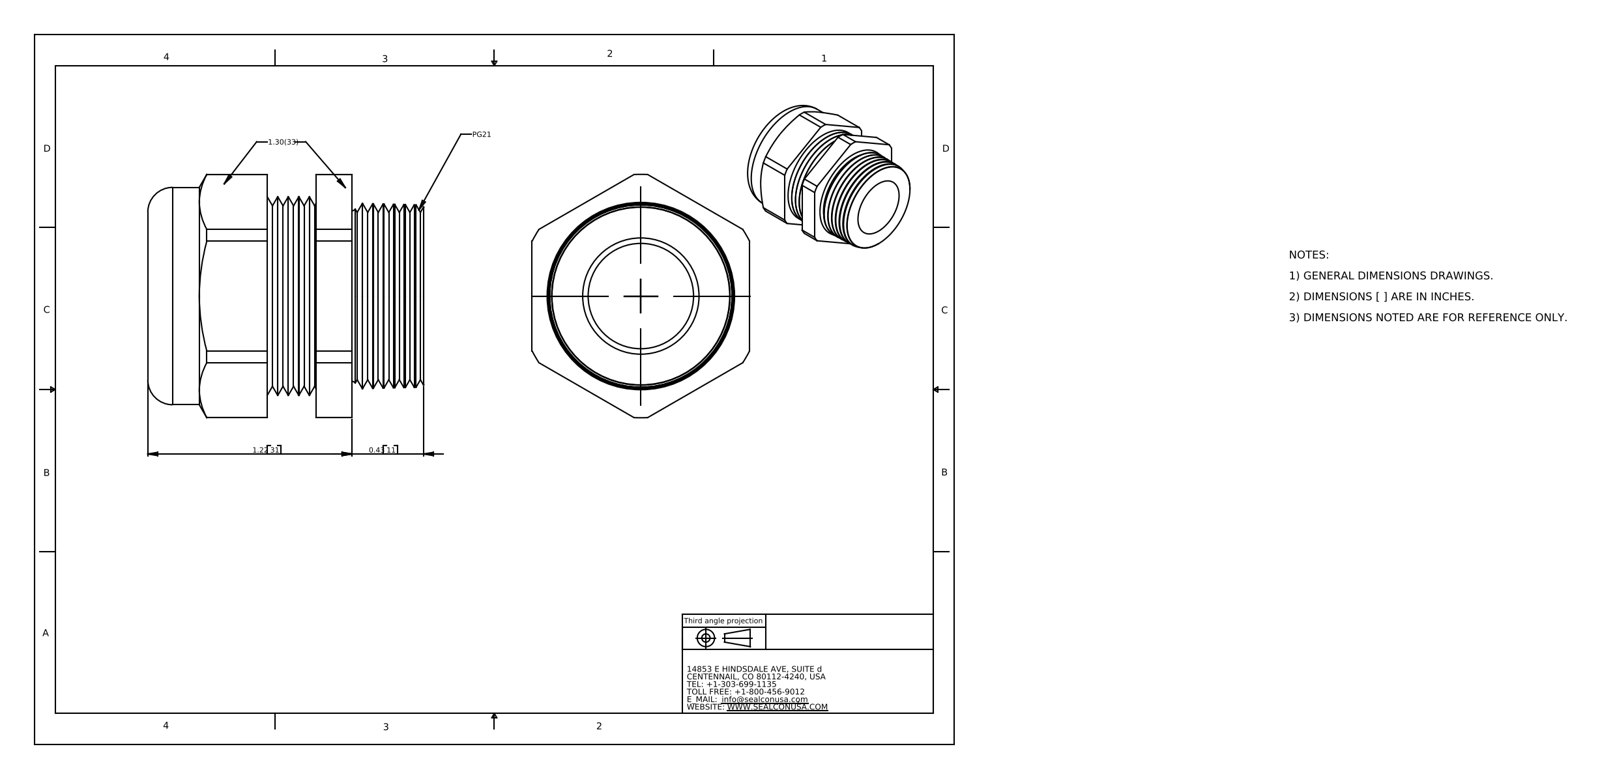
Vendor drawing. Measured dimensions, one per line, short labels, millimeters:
name: CD21AR-GY
written by: SolidWorks 2007 (CONFIG_CONTROL_DESIGN)
unit: mm
bodies: 2 solids, 130 faces (20 planar, 32 cylindrical, 78 other)
size: 41.9 × 37 × 33
volume: 22 990 mm³; area: 11 330 mm²
holes: 1× ⌀16, 1× ⌀24
bosses: 1× ⌀33, 1× ⌀30.1
rounds: 1× R18.5
face distances: 33, 34.1, 23.2, 10.9, 7.3, 30.5, 41.4, 25, 17.8, 5.4
